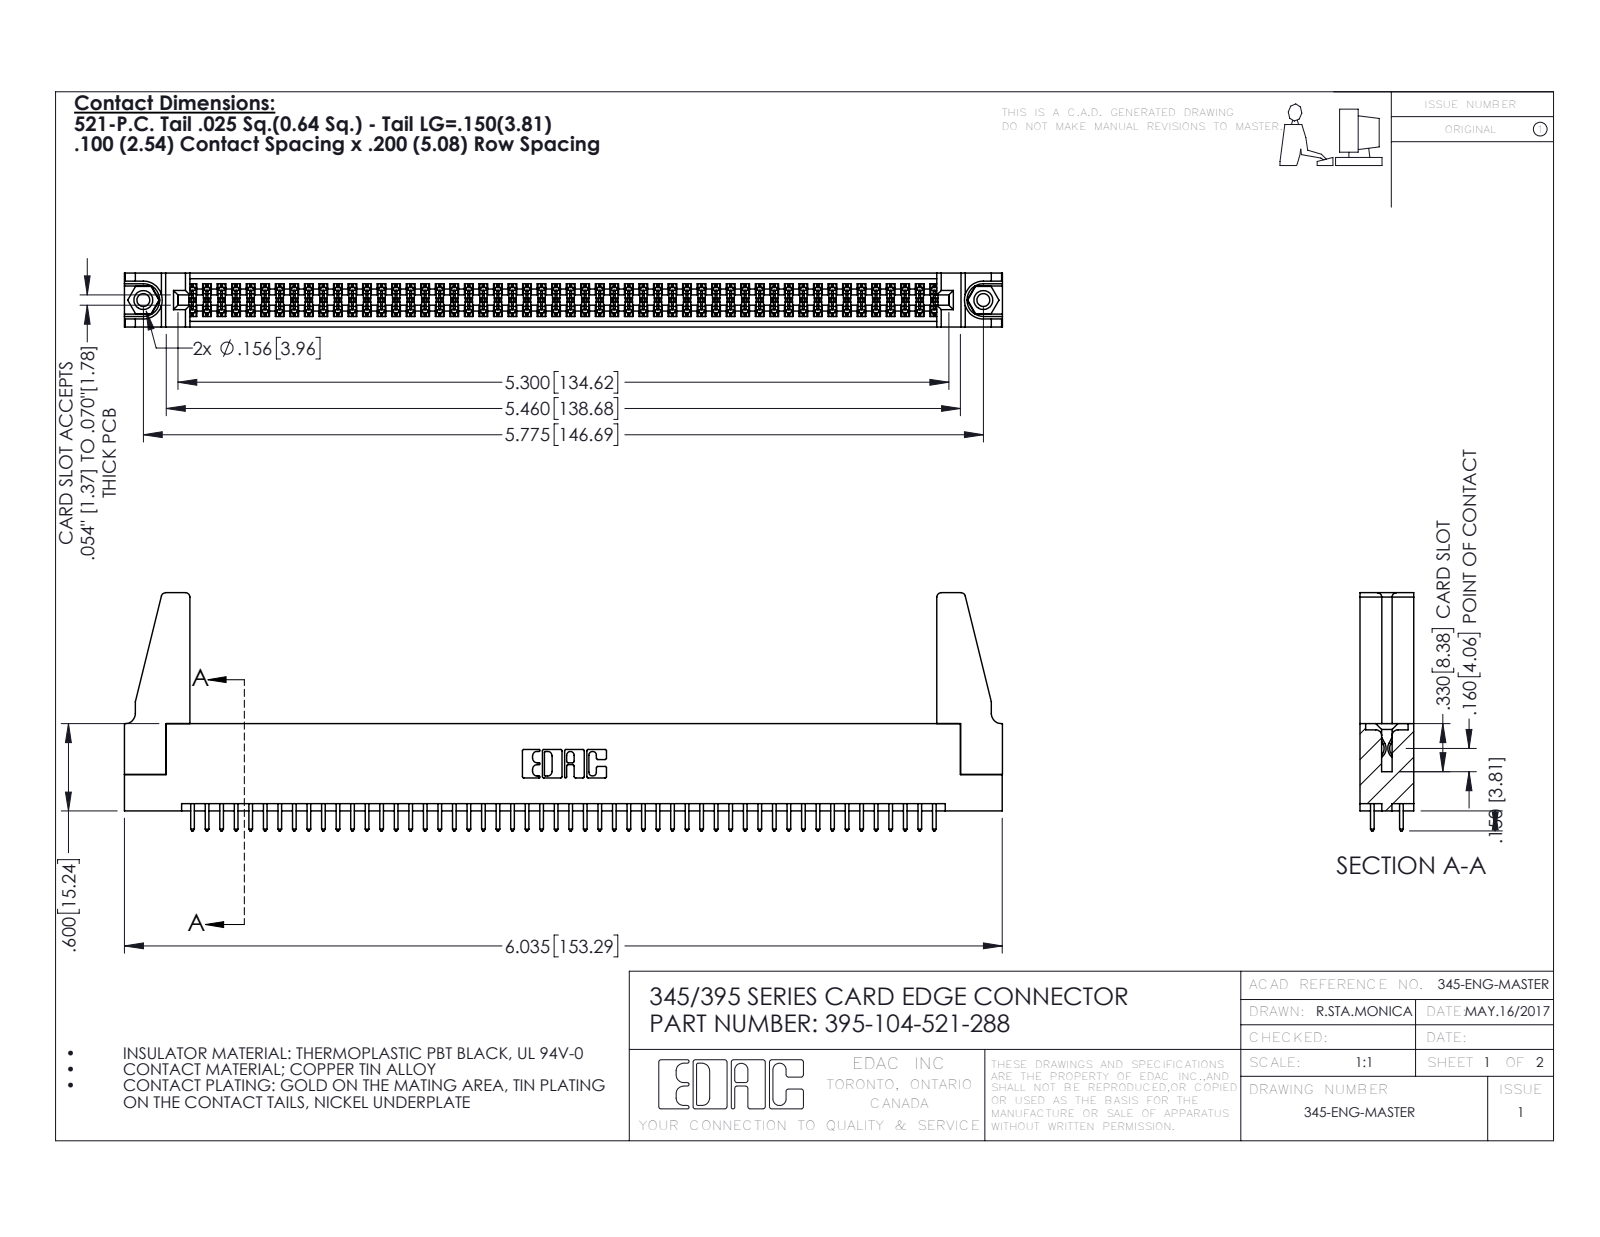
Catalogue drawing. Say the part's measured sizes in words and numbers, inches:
The part is named "345-292-001_345-293-121; 345-220-078_345-220-088; 395-104-521-288; 345-250-001_345-250-001-102 (+1 more)". Its 3-D file was written by "SolidWorks 2016 (CONFIG_CONTROL_DESIGN)". It is 109 solids with 5450 faces: 3584 planar, 1850 cylindrical and 16 other. Overall it measures 6.036 by 1.637 by 0.37 inches. Its volume is 1.11 cubic inches and its surface area 38.95 square inches. Round holes: 2 of diameter 0.089, 2 of diameter 0.125, 2 of diameter 0.156, 1 of diameter 0.064. Round bosses or shafts: 2 of diameter 0.155. Partial cylindrical surfaces (rounded edges, fillets, slot ends): 156 of radius 0.006, 104 of radius 0.01, 22 of radius 0.01, 8 of radius 0.03, 6 of radius 0.007, 6 of radius 0.031, 3 of radius 0.026, 2 of radius 0.014. The main face-to-face distances are 0.072, 0.298, 0.37, 0.2, 0.098, 0.272, 0.025, 0.225, 0.175, 0.149. The hole center spacings are 0.27, 5.539, 5.775.
